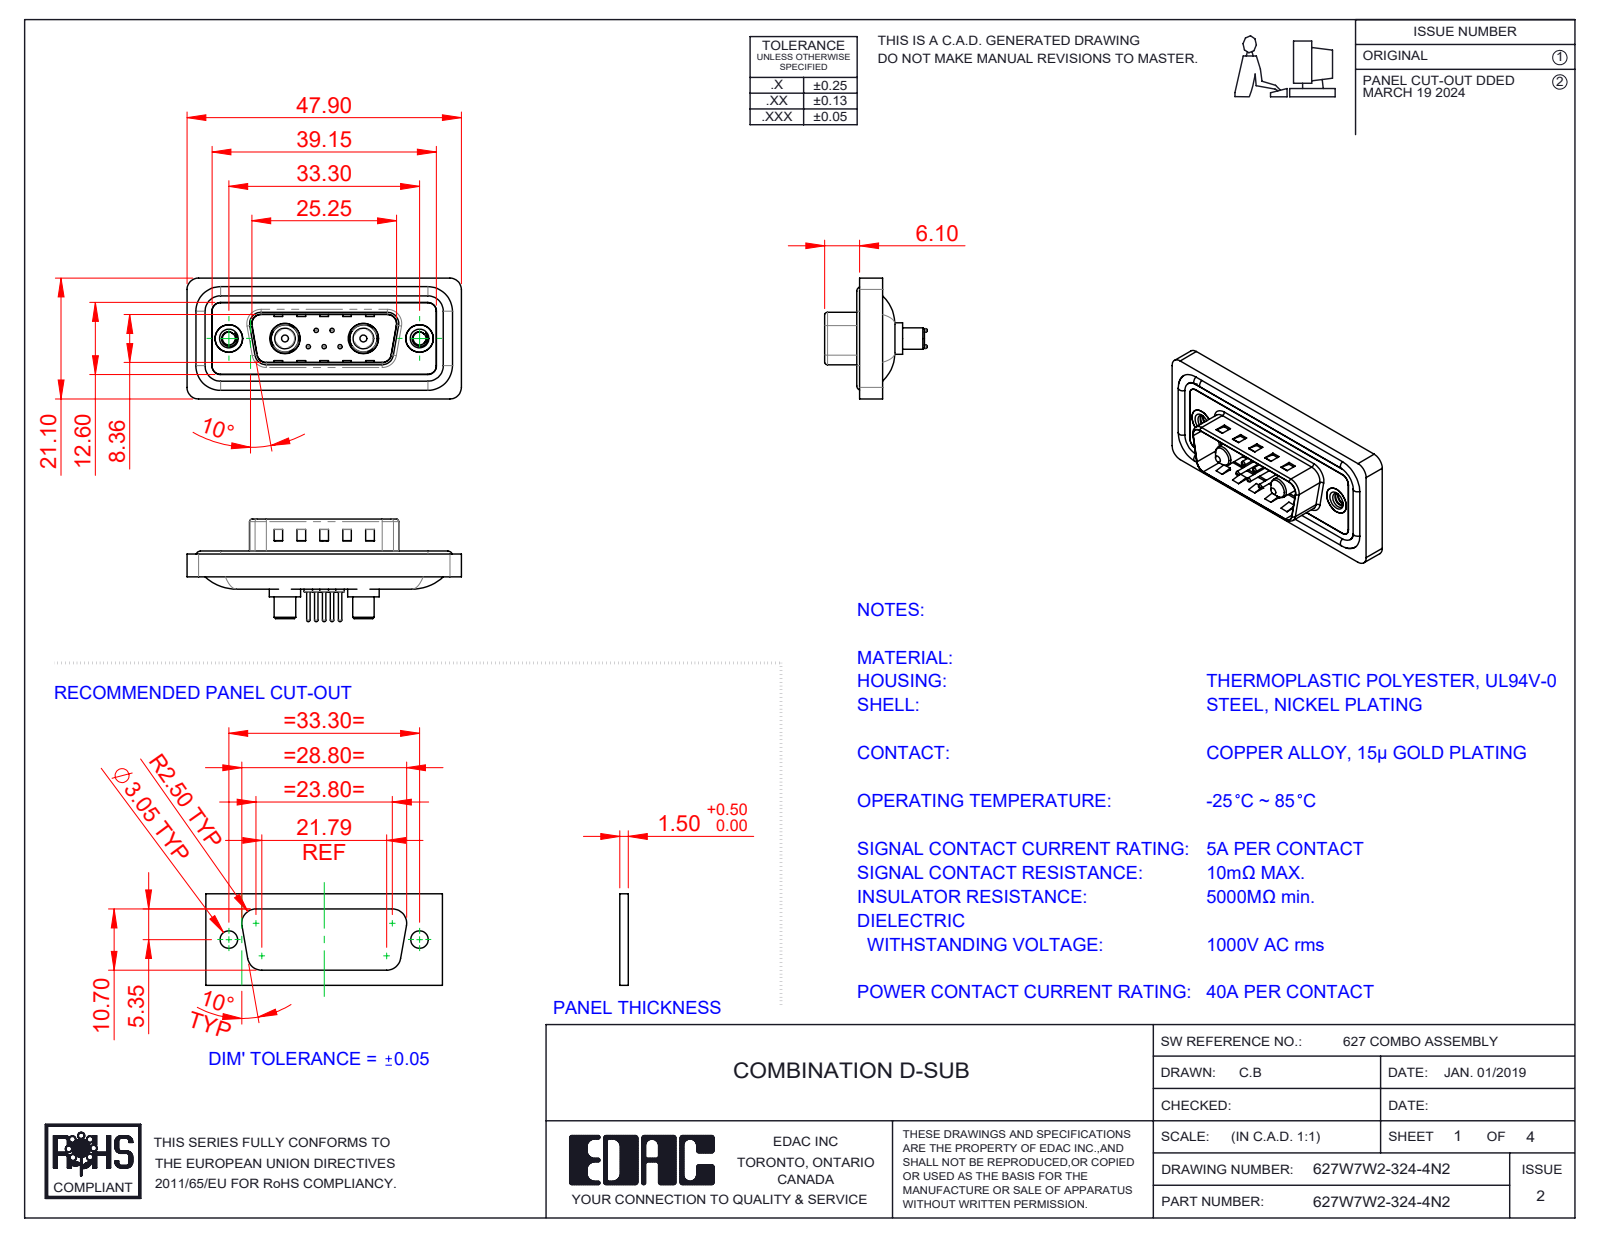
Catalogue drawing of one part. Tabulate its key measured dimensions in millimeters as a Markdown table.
| quantity | value |
| --- | --- |
| part name | 627Combo Housing_7W2; 627Combo Shell Front_15 Contacts; 627Combo Threaded Rivet_2; 627Combo Waterproof Housing_15 Contacts (+5 more) |
| STEP written by | SolidWorks 2023 (CONFIG_CONTROL_DESIGN) |
| units | millimeters |
| bodies | 16 solids, 710 faces (232 planar, 292 cylindrical, 186 other) |
| overall size | 47.9 × 21.1 × 17.9 |
| volume | 5 554 mm³ |
| surface area | 8 815 mm² |
| round holes (diameter × count) | 0.75 × 5, 1.6 × 5, 2 × 5, 2.26 × 2, 4 × 2, 4.8 × 2, 4.85 × 2, 5 × 2, 5.3 × 2 |
| round bosses / shafts (diameter × count) | 1.5 × 5, 0.6 × 5, 1.6 × 4, 5.5 × 2, 5.2 × 2, 4.9 × 2, 4.75 × 2, 3.75 × 2 |
| partial cylindrical surfaces (radius × count) | 1.5 × 26, 2 × 20, 0.5 × 8, 1.6 × 8, 0.25 × 4, 0.6 × 4, 0.65 × 4, 0.9 × 4 |
| main face-to-face distances | 0.4, 1.1, 1.6, 1.5, 0.5, 3.1, 2.9, 0.82, 9.58, 2.5 |
| hole center spacings | 3.16, 2.77, 9.8, 23.5, 4.31, 4.33, 5.03, 5.04 |
